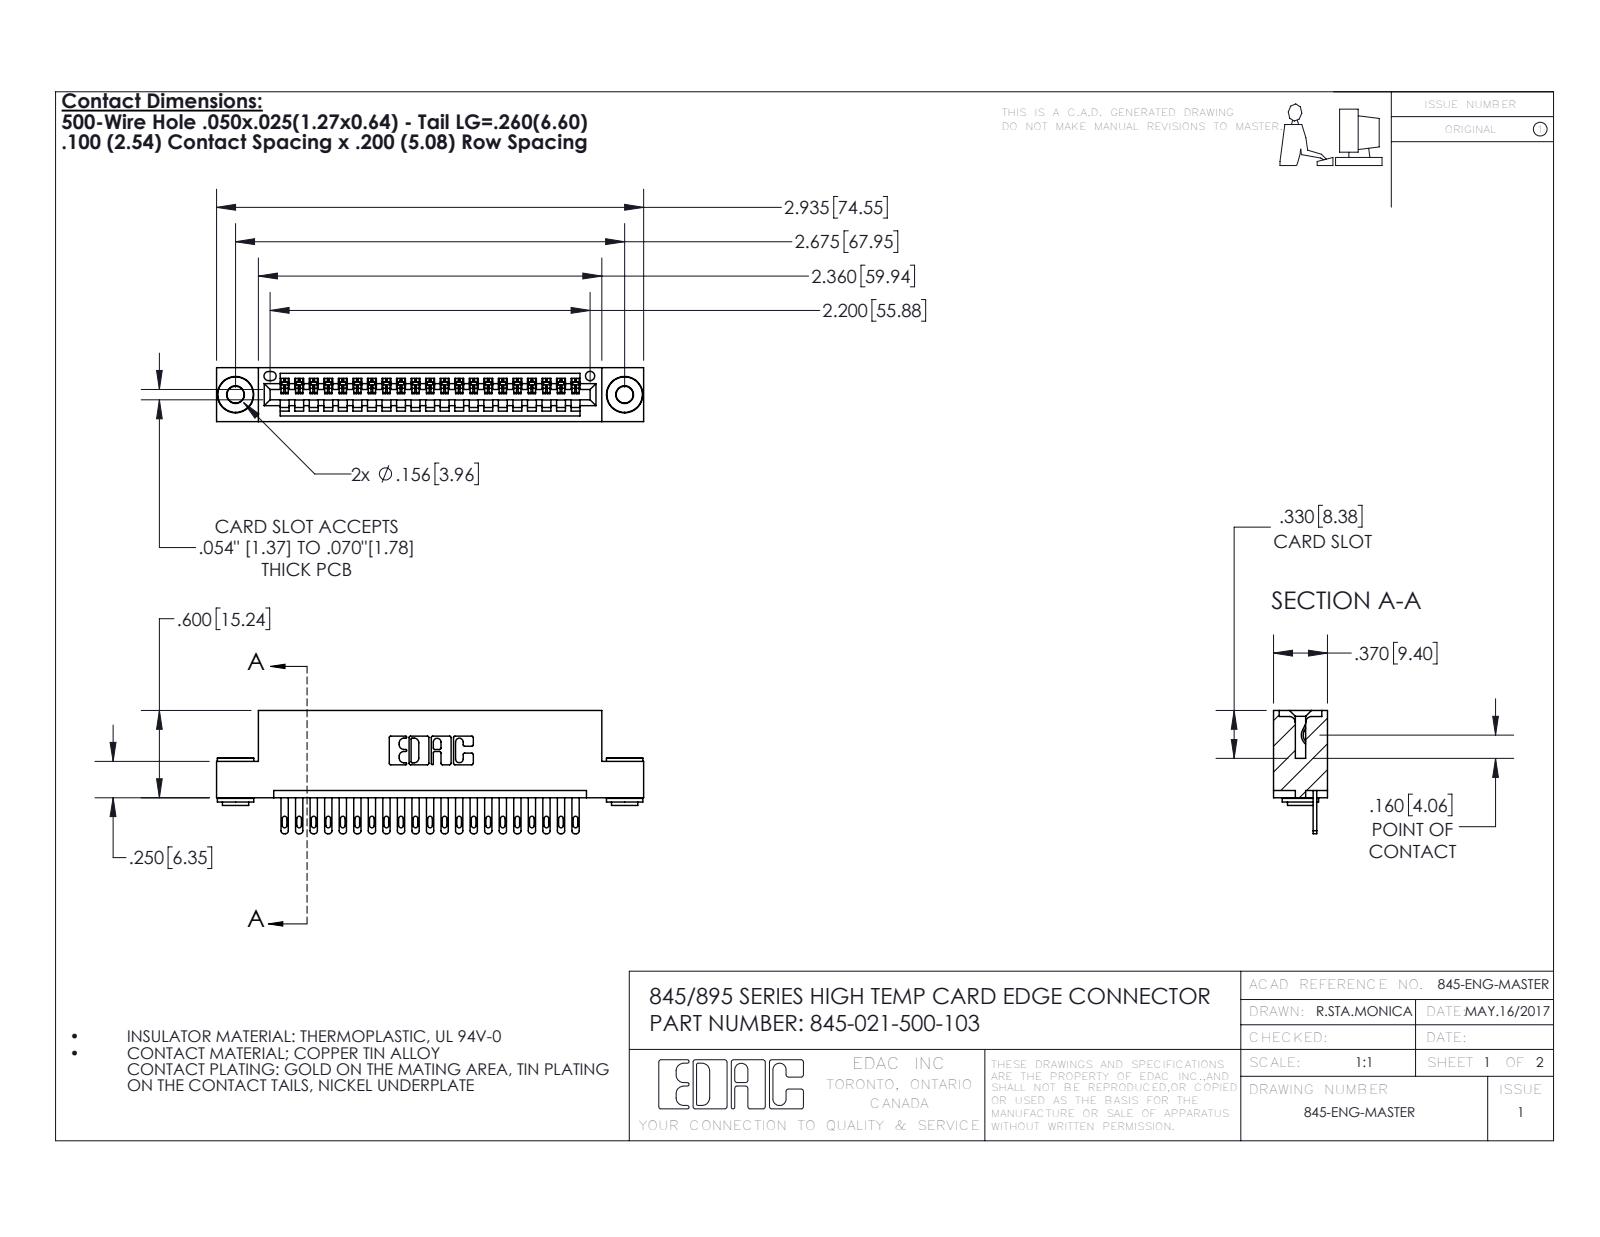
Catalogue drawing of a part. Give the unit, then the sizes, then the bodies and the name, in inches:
Units: inches
Overall size (bounding box): 2.935 × 0.847 × 0.37
Round holes (diameter × count): ⌀0.116 ×2, ⌀0.156 ×2, ⌀0.064 ×1
Round bosses / shafts (diameter × count): ⌀0.25 ×2, ⌀0.18 ×2, ⌀0.136 ×2
Partial cylindrical surfaces — rounded edges, fillets, slot ends (radius × count): R0.006 ×42, R0.016 ×42, R0.02 ×42, R0.01 ×22, R0.007 ×6, R0.031 ×6, R0.026 ×3, R0.031 ×2
Main face-to-face distances: 0.072, 0.298, 0.2, 0.37, 0.025, 0.098, 0.272, 0.225, 0.149, 0.072
Hole centre spacings: 0.27, 2.441, 2.675
Volume: 0.424 in³ · Surface area: 14.26 in²
Bodies: 24 solids, 1298 faces (804 planar, 486 cylindrical, 8 other)
Part name (STEP PRODUCT): 345-250-002_345-250-002-102; 345 Part_Flush Mounting Lugs - 0.156 Dia-TH; 345-292-001_345-293-100; 345-021-500-103
STEP written by: SolidWorks 2016 (CONFIG_CONTROL_DESIGN)
